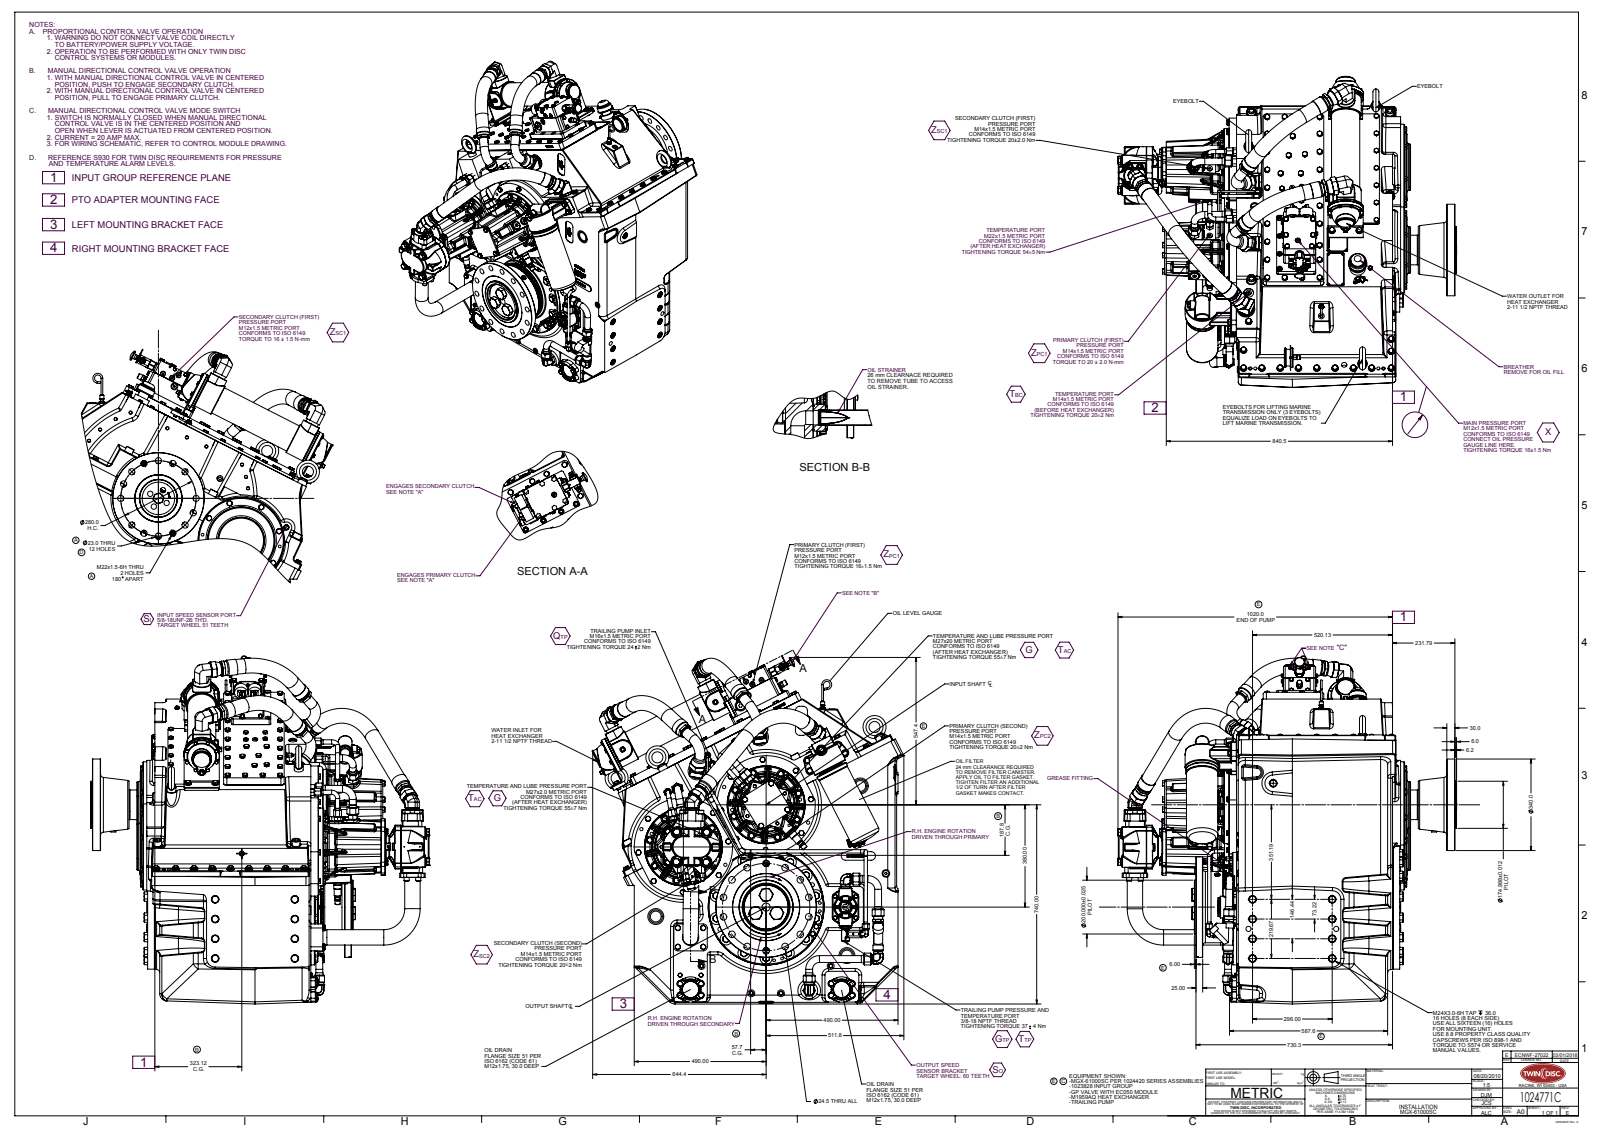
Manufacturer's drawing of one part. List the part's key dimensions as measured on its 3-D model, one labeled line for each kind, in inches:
Part name (STEP PRODUCT): 1024771C
STEP written by: SolidWorks 2015 (AUTOMOTIVE_DESIGN)
Units: inches
Bodies: 0 solids, 6422 faces (2864 planar, 1625 cylindrical, 1933 other)
Overall size (bounding box): 55.343 × 49.528 × 45.512
Round holes (diameter × count): ⌀0.472 ×36, ⌀0.65 ×16, ⌀1.102 ×16, ⌀0.965 ×14, ⌀0.906 ×12, ⌀1.112 ×9, ⌀0.787 ×8, ⌀0.394 ×6, ⌀0.402 ×5, ⌀0.504 ×5, ⌀1.752 ×5, ⌀0.501 ×4
Round bosses / shafts (diameter × count): ⌀0.709 ×32, ⌀0.945 ×29, ⌀0.75 ×9, ⌀1.081 ×8, ⌀1 ×8, ⌀0.744 ×8, ⌀0.603 ×8, ⌀1.47 ×7
Partial cylindrical surfaces — rounded edges, fillets, slot ends (radius × count): R0.472 ×159, R0.118 ×123, R0.236 ×103, R1.71 ×82, R0.12 ×62, R0.1 ×41, R0.059 ×36, R0.06 ×26
Main face-to-face distances: 0.252, 22.103, 21.85, 23.87, 23.617, 1.767, 0.714, 1.212, 1.181, 1.091
Hole centre spacings: 5.512, 10.184, 4.219, 7.795, 2.15, 2.151, 6.124, 6.124
